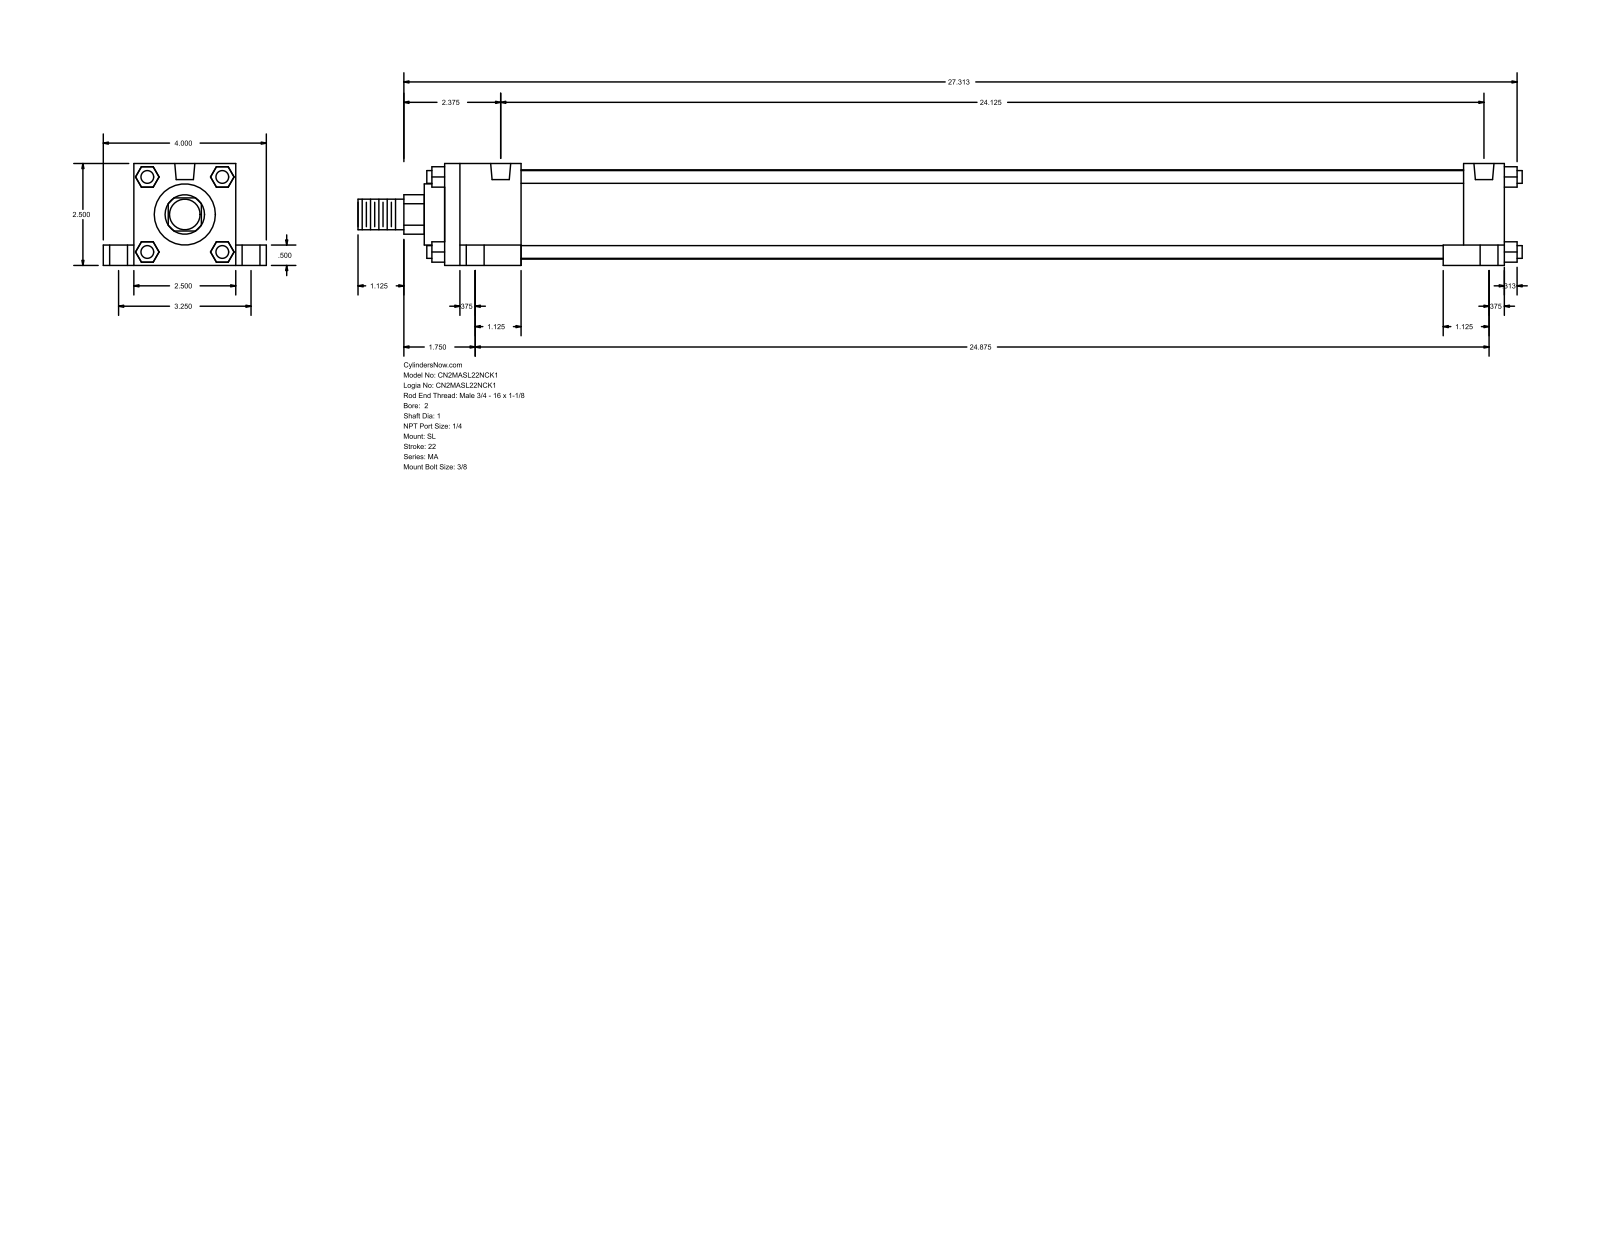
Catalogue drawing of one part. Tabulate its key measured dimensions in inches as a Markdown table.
| quantity | value |
| --- | --- |
| part name | MA_SL__0200_1 |
| STEP written by | GSSL Pune (CONFIG_CONTROL_DESIGN) |
| units | inches |
| bodies | 0 solids, 148 faces (112 planar, 36 cylindrical, 0 other) |
| overall size | 28.563 × 4 × 2.5 |
| round holes (diameter × count) | 0.313 × 4, 0.437 × 4, 0.687 × 4, 0.492 × 2 |
| round bosses / shafts (diameter × count) | 0.313 × 4, 2.19 × 1, 1.5 × 1, 1 × 1, 0.75 × 1 |
| partial cylindrical surfaces (radius × count) | 0.484 × 1 |
| main face-to-face distances | 2.5, 0.5, 26, 0.75, 3.25, 1, 2, 1.875, 24.125, 25 |
| hole center spacings | 1.63, 1.741, 3.25, 24.125, 24.304, 24.803, 24.875, 25.086 |
